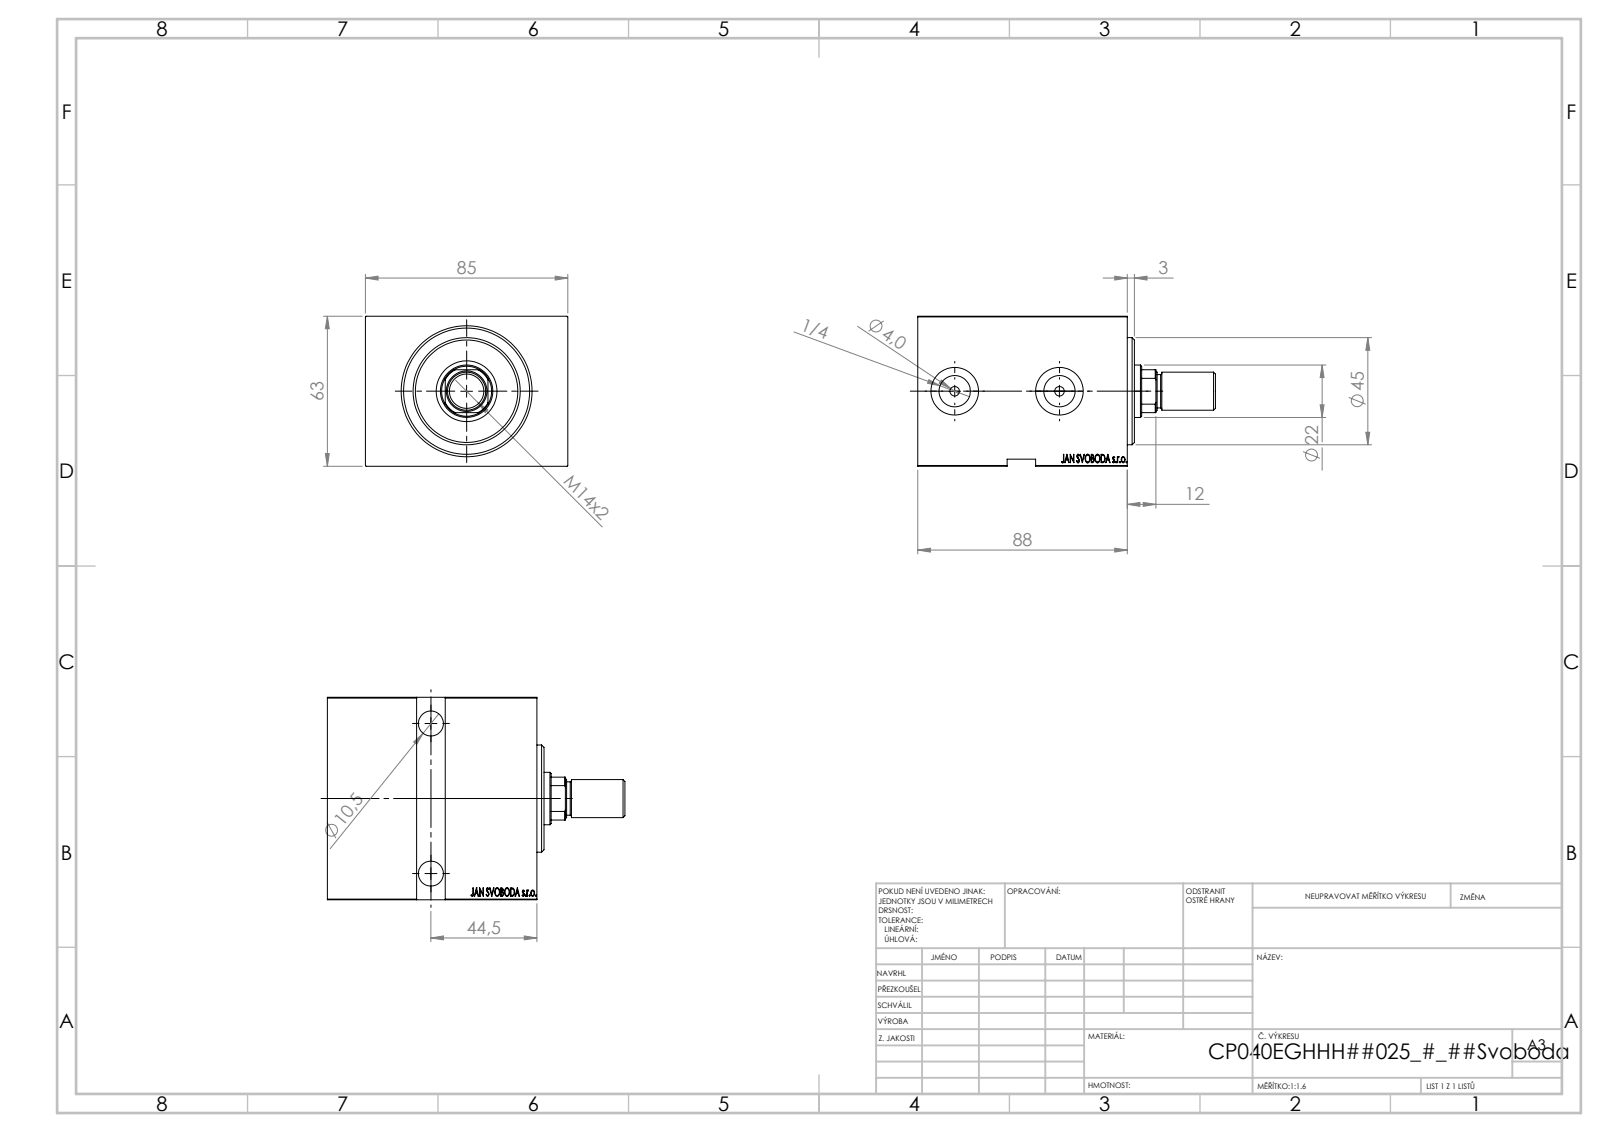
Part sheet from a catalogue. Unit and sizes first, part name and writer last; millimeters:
Units: millimetres
Overall size (bounding box): 125 × 85 × 63
Round holes (diameter × count): ⌀4 ×2, ⌀10.5 ×2, ⌀13.16 ×2, ⌀16.5 ×2, ⌀20 ×2, ⌀12.5 ×1, ⌀22 ×1, ⌀25.5 ×1, ⌀40 ×1, ⌀53 ×1
Round bosses / shafts (diameter × count): ⌀45 ×1, ⌀42 ×1, ⌀16 ×1, ⌀14 ×1
Partial cylindrical surfaces — rounded edges, fillets, slot ends (radius × count): R10.5 ×1
Main face-to-face distances: 63, 85, 88, 12, 76, 3, 5, 83, 71, 37
Hole centre spacings: 44, 63
Volume: 442 976 mm³ · Surface area: 73 452 mm²
Bodies: 4 solids, 860 faces (412 planar, 48 cylindrical, 400 other)
Part name (STEP PRODUCT): V450CM_MALE_METRIC; V450CM_E_VCP; V450CM_VC_B; V450CM_E_Body
STEP written by: SolidWorks 2019 (CONFIG_CONTROL_DESIGN)
